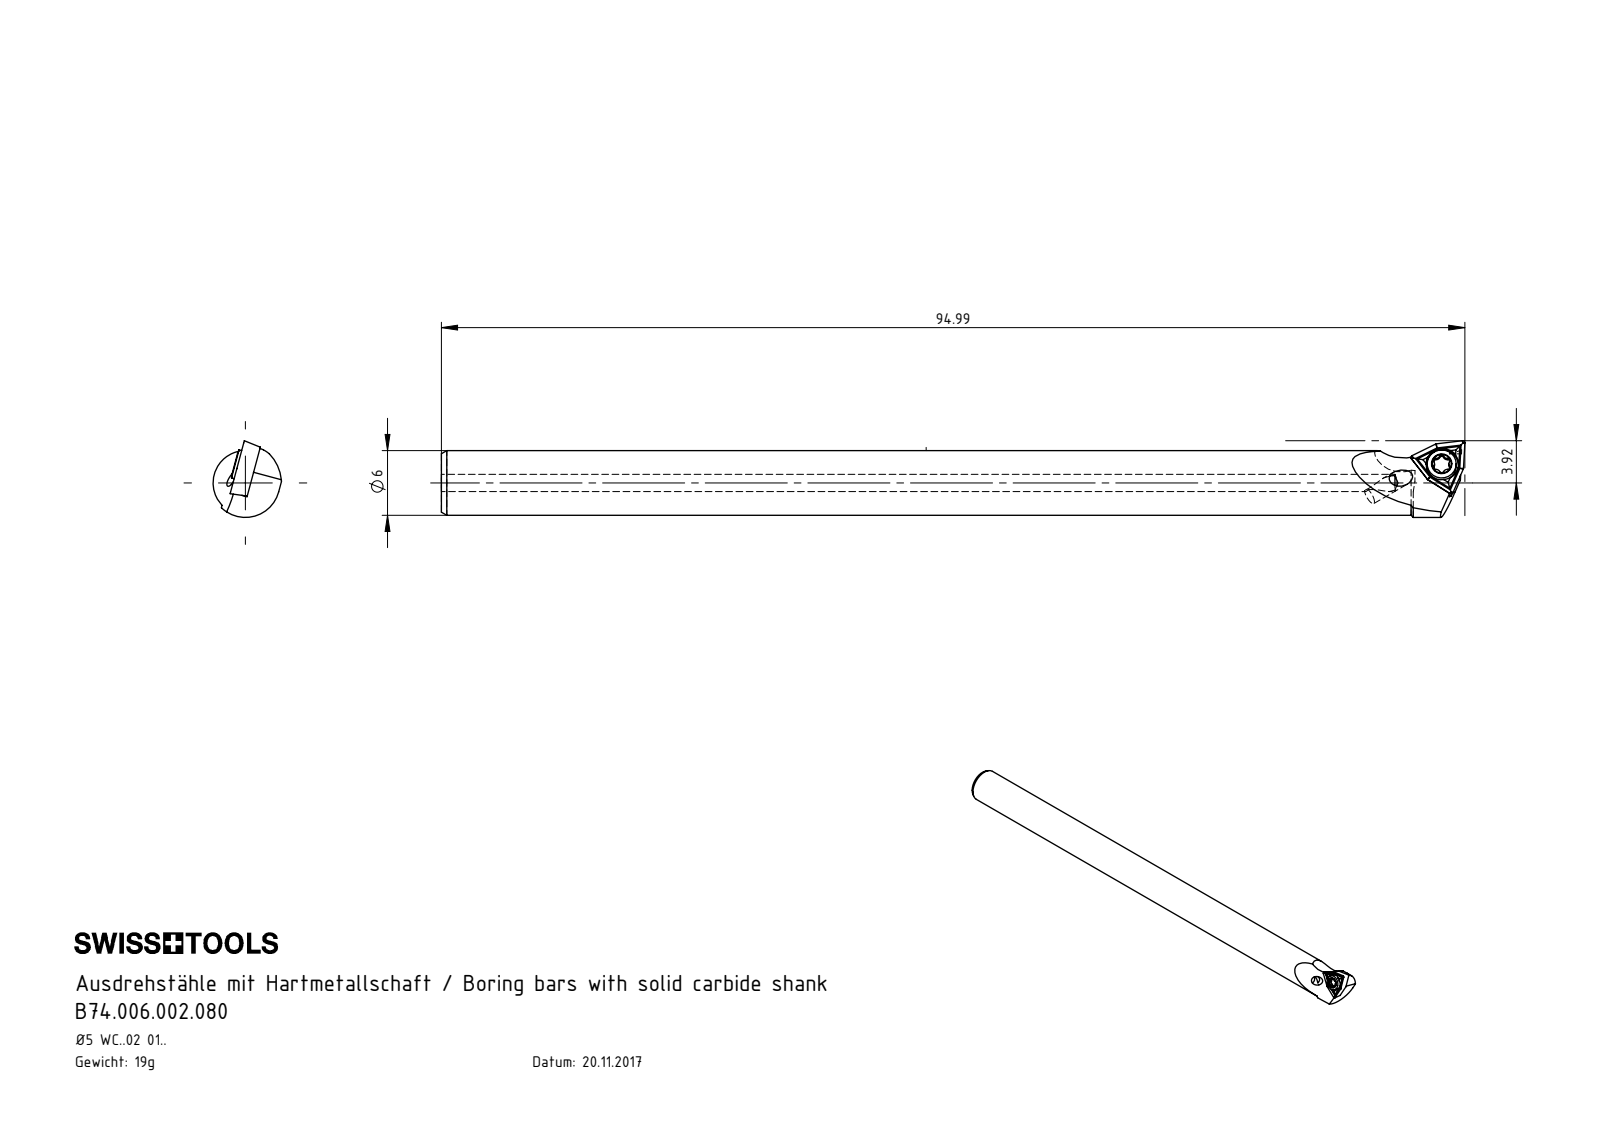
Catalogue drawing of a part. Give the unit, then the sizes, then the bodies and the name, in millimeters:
Units: millimetres
Overall size (bounding box): 85.99 × 5.32 × 5
Round holes (diameter × count): ⌀1.6 ×3, ⌀2.3 ×1, ⌀3 ×1
Round bosses / shafts (diameter × count): ⌀5 ×1, ⌀2.7 ×1, ⌀2 ×1
Partial cylindrical surfaces — rounded edges, fillets, slot ends (radius × count): R0.21 ×6, R0.36 ×6, R0.8 ×1
Main face-to-face distances: 1.49, 1.39, 1.61, 3, 3.1, 3.2, 1.59, 3.5, 1.89, 0.5
Volume: 1 477 mm³ · Surface area: 1 854 mm²
Bodies: 3 solids, 106 faces (36 planar, 33 cylindrical, 37 other)
Part name (STEP PRODUCT): B06-WWA.K11.080_A; B74.006.002.080; SFS-Torx-M2; WCMT020102
STEP written by: SolidWorks 2017 (CONFIG_CONTROL_DESIGN)
